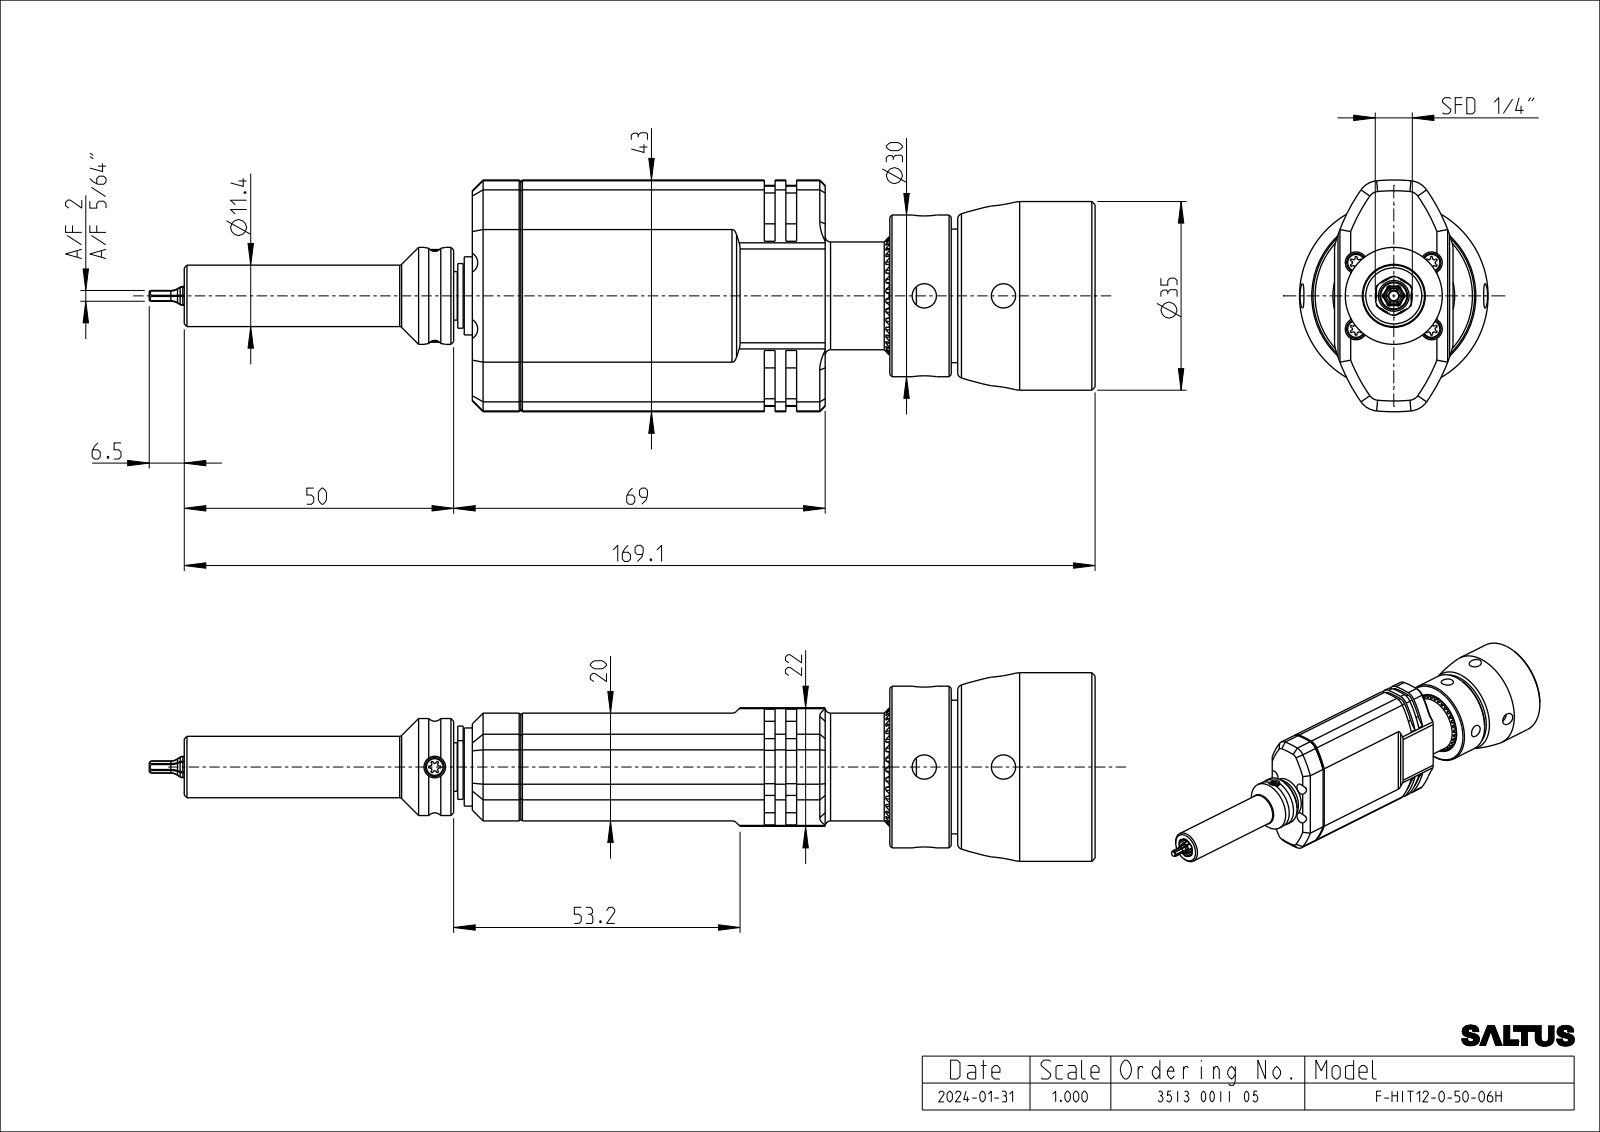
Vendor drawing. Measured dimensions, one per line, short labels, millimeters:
name: 3513001105_SW0001
written by: CREO PARAMETRIC BY PTC INC, 2022414 (AP242_MANAGED_MODEL_BASED_3D_ENGINEERING_MIM_LF)
unit: mm
bodies: 1 solid, 789 faces (240 planar, 339 cylindrical, 210 other)
size: 175.6 × 43 × 35
volume: 92 470 mm³; area: 18 560 mm²
holes: 5× ⌀4, 4× ⌀4.5, 2× ⌀1.2, 1× ⌀9.1
bosses: 5× ⌀3.5, 1× ⌀35, 1× ⌀30, 1× ⌀24.8, 1× ⌀20, 1× ⌀18, 1× ⌀14.5, 1× ⌀12
rounds: 42× R0.2, 30× R0.3, 18× R1, 12× R2.5, 8× R4, 6× R0.8, 6× R33, 6× R34
face distances: 20, 1, 21, 50.1, 115.6, 65.5, 38.1, 12, 77.5, 22
hole spacings: 9.3, 4.5, 6.2, 8.1, 12.3, 13.6, 14, 14.7
